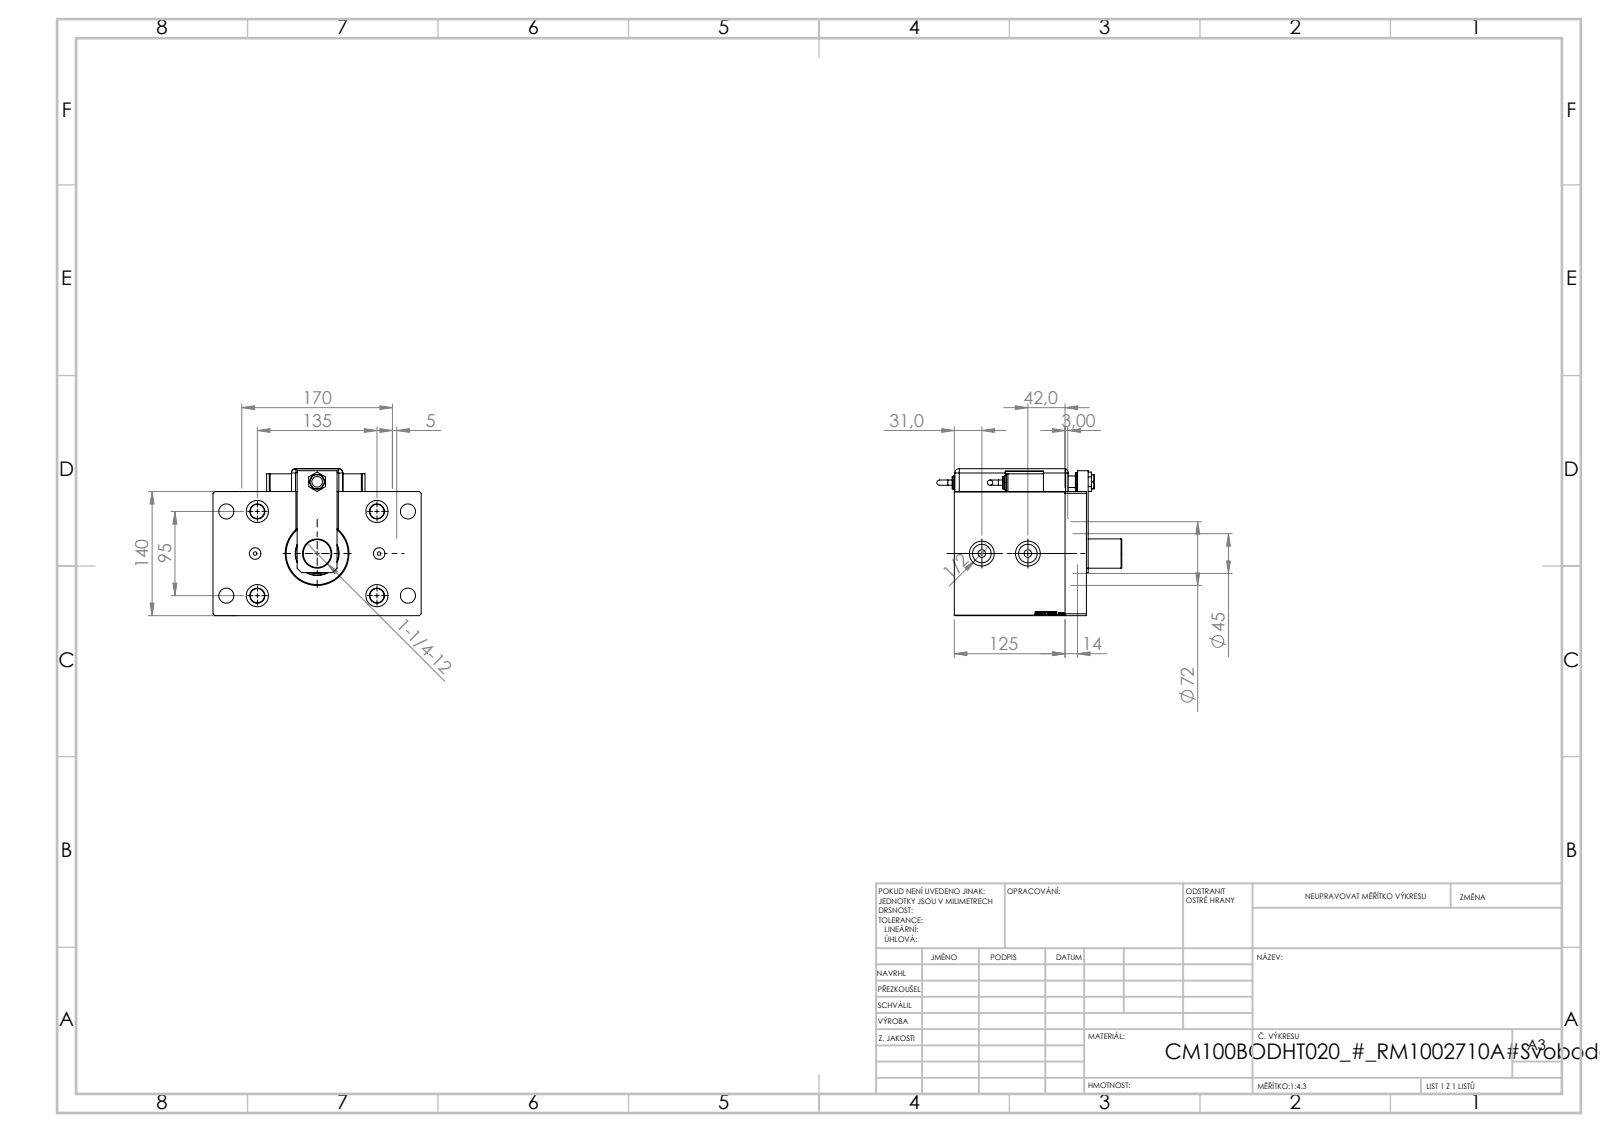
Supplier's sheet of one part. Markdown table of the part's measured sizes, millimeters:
| quantity | value |
| --- | --- |
| part name | MAGNETIC SWITCH Q; Zatka_OIL_PORT; V450CM_VC_B; FLANGE (+7 more) |
| STEP written by | SolidWorks 2019 (CONFIG_CONTROL_DESIGN) |
| units | millimeters |
| bodies | 17 solids, 1387 faces (665 planar, 163 cylindrical, 559 other) |
| overall size | 235 × 208.76 × 165.8 |
| volume | 3 677 000 mm³ |
| surface area | 386 586 mm² |
| round holes (diameter × count) | 17 × 8, 4 × 4, 16 × 4, 25 × 4, 13 × 3, 8 × 2, 8.5 × 2, 20.96 × 2, 28 × 2, 12 × 1, 14 × 1, 31.5 × 1 |
| round bosses / shafts (diameter × count) | 20 × 3, 26 × 2, 16 × 2, 14 × 2, 6 × 2, 31 × 1 |
| partial cylindrical surfaces (radius × count) | 5 × 9, 10 × 1, 22 × 1 |
| main face-to-face distances | 140, 125, 24, 149, 51, 170, 75, 74, 3, 10 |
| hole center spacings | 35, 47.57, 57.55, 82.54, 95, 101.24, 112.97, 145.47 |
